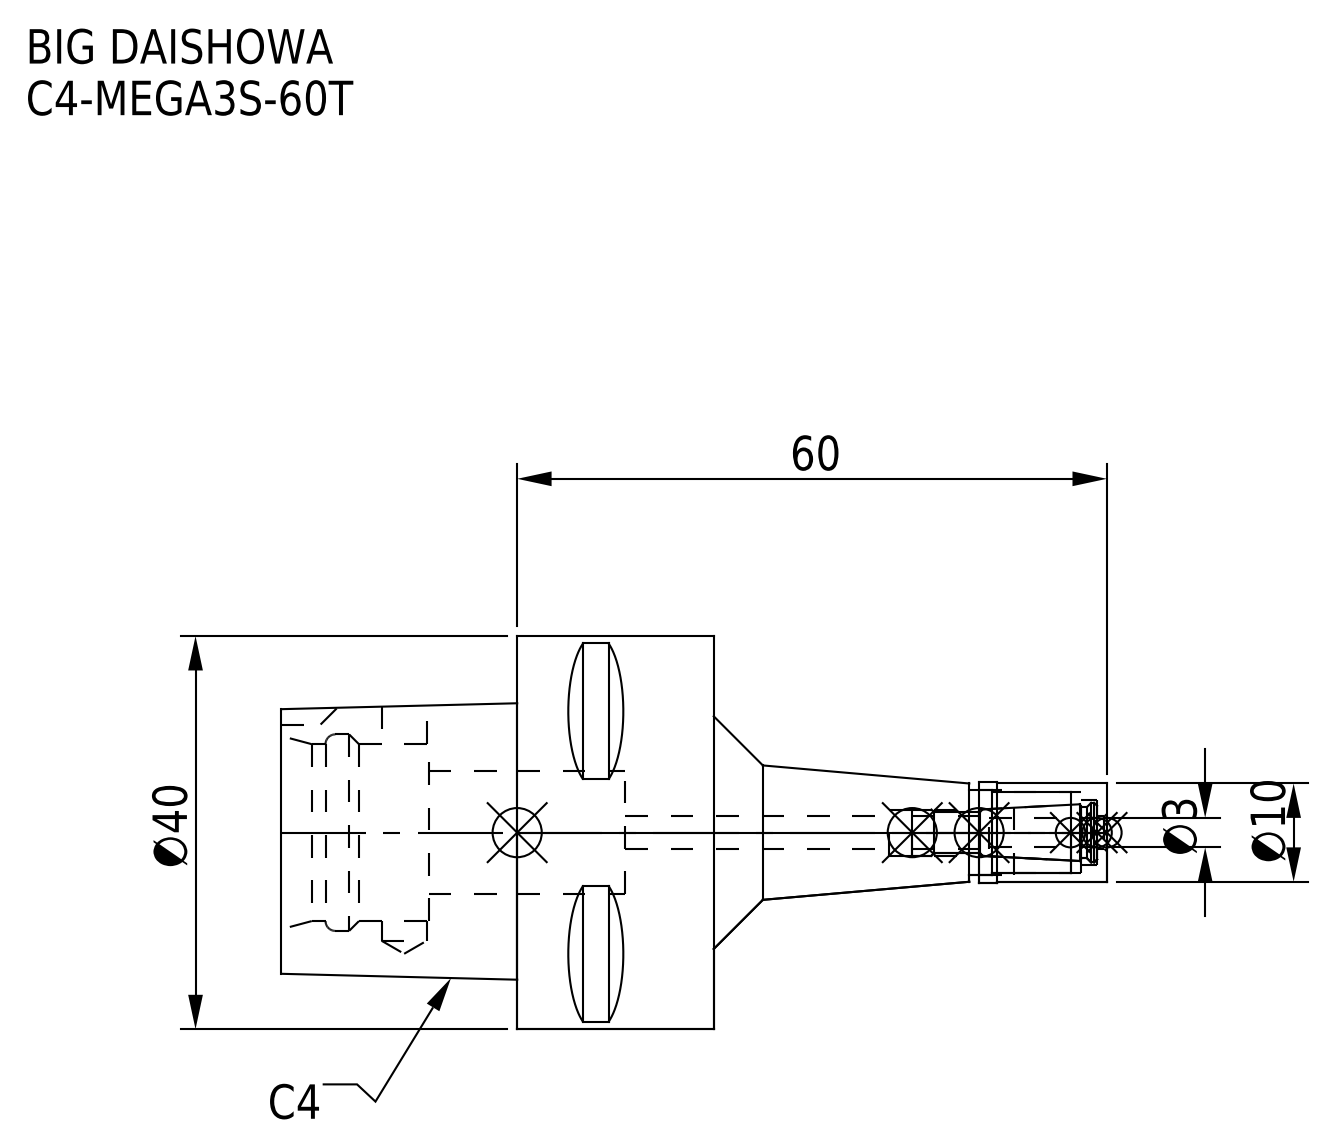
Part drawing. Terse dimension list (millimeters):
name: MGN3S_1.stp; C4-MEGA3S-60T; C4-MEGA3S-60T-030.stp; C4-MEGA3S-60T-030_ASM.stp (+3 more)
written by: SolidWorks 2019 (CONFIG_CONTROL_DESIGN)
unit: mm
bodies: 2 solids, 90 faces (37 planar, 35 cylindrical, 18 other)
size: 84 × 40 × 40
volume: 36 193 mm³; area: 11 431 mm²
holes: 1× ⌀3.3, 1× ⌀3.4, 1× ⌀4.6, 1× ⌀4.7, 1× ⌀6.6, 1× ⌀8.2, 1× ⌀8.7, 1× ⌀12.5, 1× ⌀18, 1× ⌀20
bosses: 1× ⌀40, 1× ⌀10.3, 1× ⌀10
rounds: 1× R3
face distances: 20, 9, 44, 24, 35, 29, 15, 15.52, 11, 34.9
